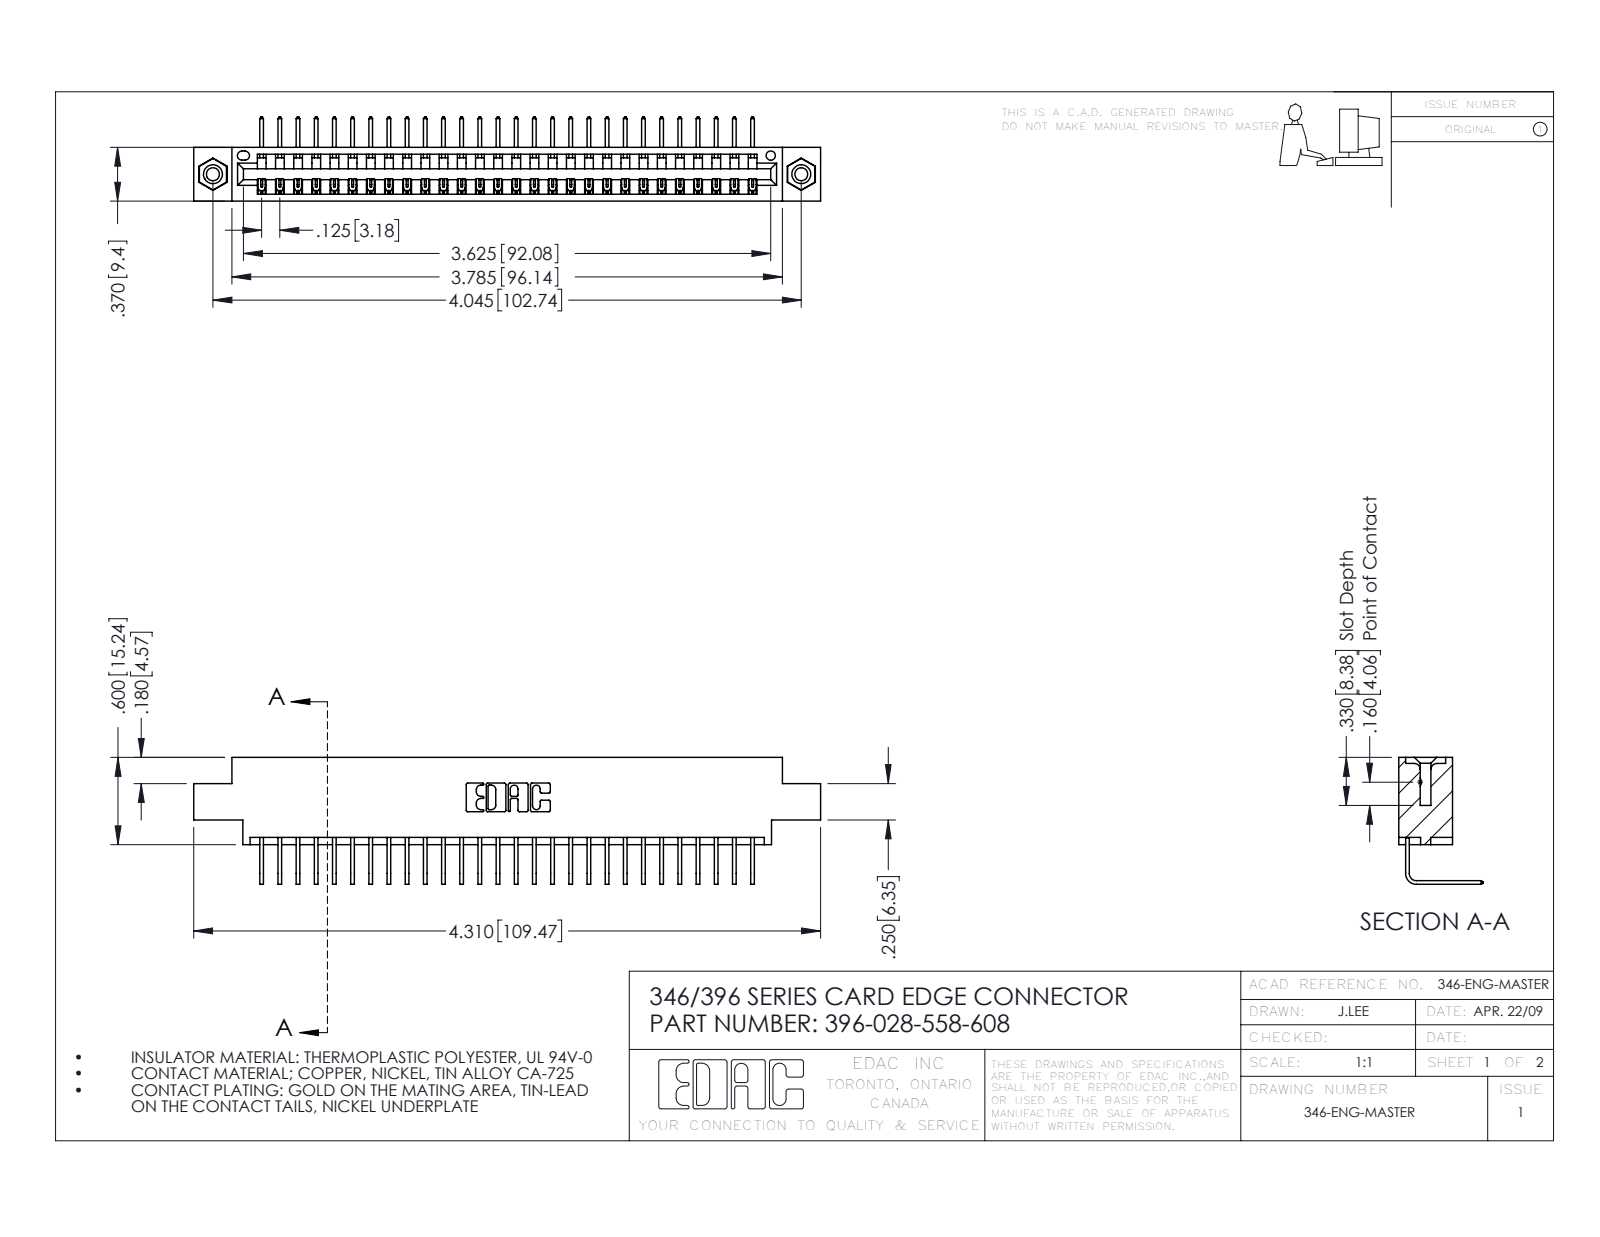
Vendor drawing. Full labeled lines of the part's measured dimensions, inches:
Part name (STEP PRODUCT): 346 Part_0.170 Offset - 0.156 Dia-TI; 396-028-558-608; 345-292-001_558 Tail - 2; 345-250-001_345-250-003-102
STEP written by: SolidWorks 2016 (CONFIG_CONTROL_DESIGN)
Units: inches
Bodies: 31 solids, 1866 faces (1288 planar, 562 cylindrical, 16 other)
Overall size (bounding box): 4.31 × 0.873 × 0.58
Volume: 0.629 in³ · Surface area: 20.89 in²
Round holes (diameter × count): ⌀0.089 ×2, ⌀0.125 ×2, ⌀0.156 ×2, ⌀0.064 ×1
Round bosses / shafts (diameter × count): ⌀0.155 ×2
Partial cylindrical surfaces — rounded edges, fillets, slot ends (radius × count): R0.006 ×56, R0.01 ×22, R0.007 ×6, R0.031 ×6, R0.026 ×3, R0.031 ×2, R0.04 ×2, R0.014 ×1
Main face-to-face distances: 0.322, 0.048, 0.37, 0.25, 0.298, 0.025, 0.072, 0.222, 0.148, 0.1
Hole centre spacings: 0.246, 3.837, 4.045
